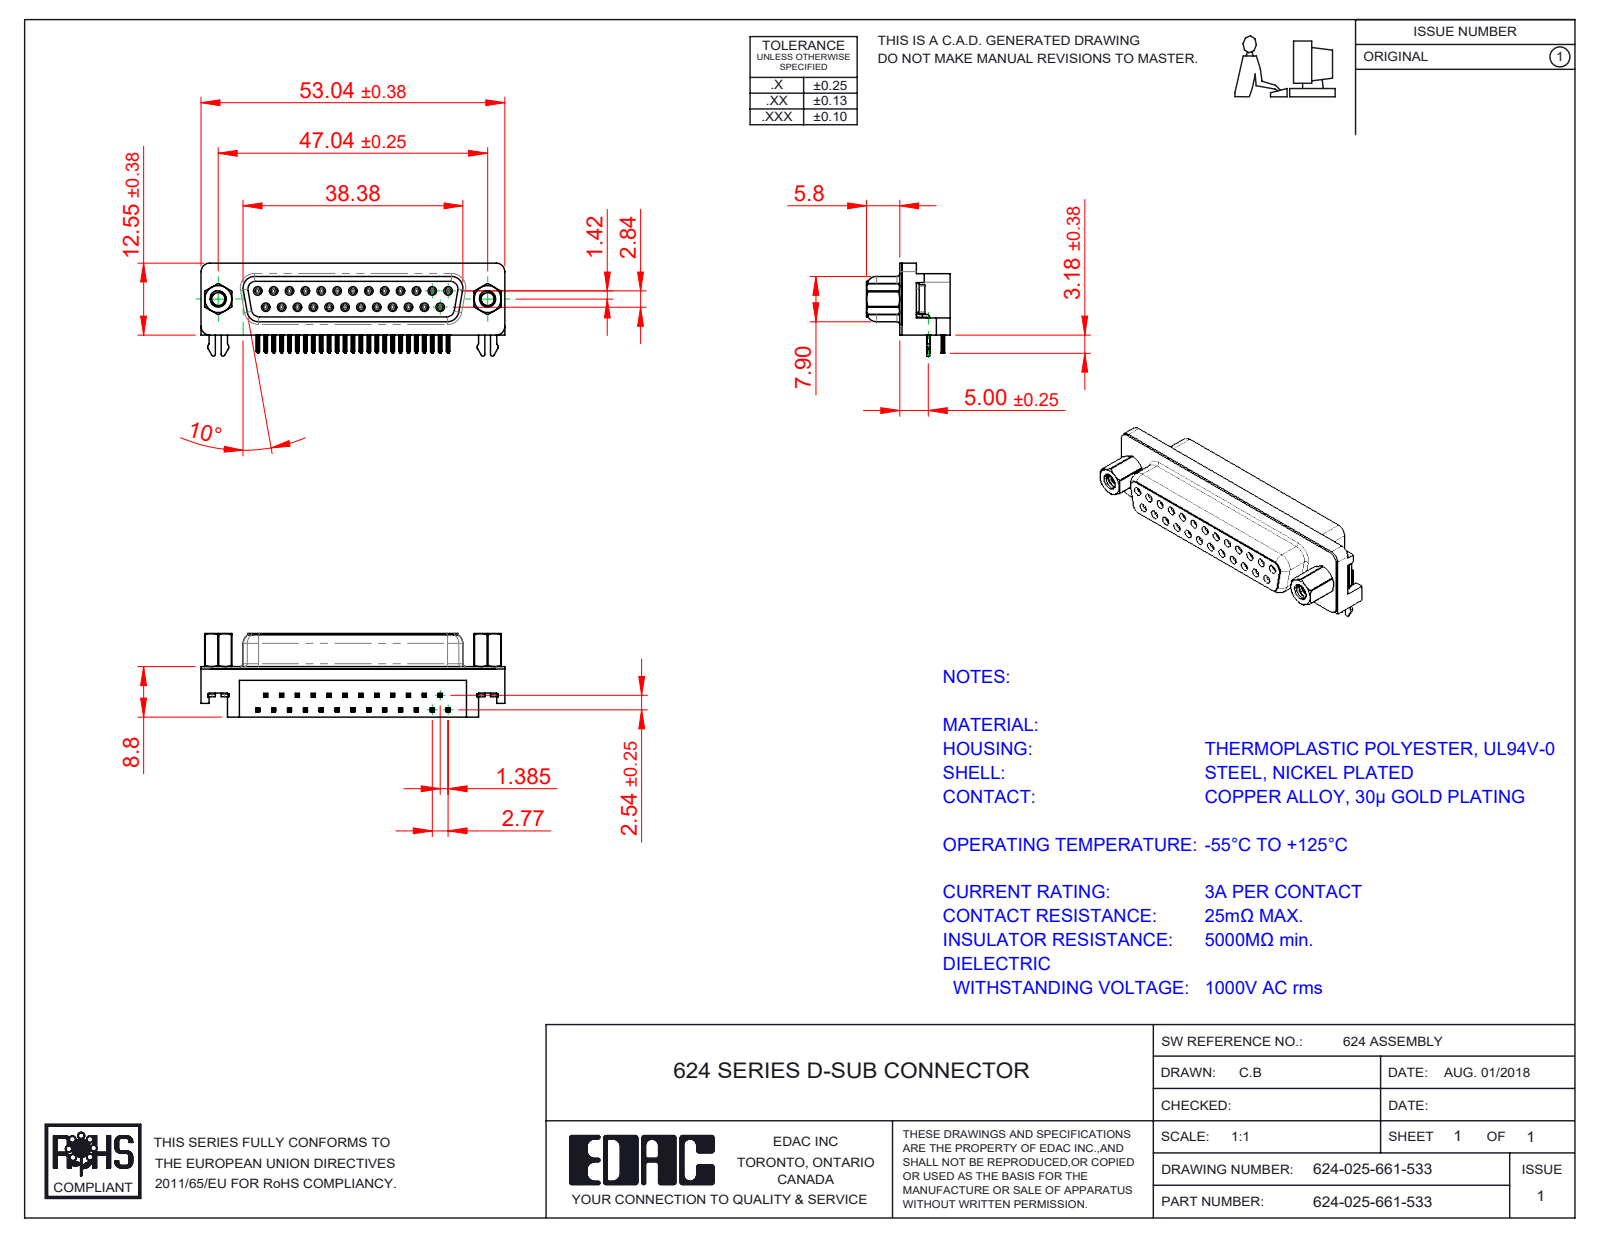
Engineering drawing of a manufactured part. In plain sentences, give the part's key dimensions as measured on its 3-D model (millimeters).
The part is named "624 Socket Bottom; 624-025-661-533; 624 Housing_25 Socket; 624 4-40 Threaded Rivet (+4 more)". Its 3-D file was written by "SolidWorks 2016 (CONFIG_CONTROL_DESIGN)". It is 33 solids with 3876 faces: 1652 planar, 982 cylindrical and 1242 other. Overall it measures 53.04 by 16.25 by 14.6 millimeters. Its volume is 6 170 cubic millimeters and its surface area 8 748 square millimeters. Round holes: 25 of diameter 0.8, 25 of diameter 0.9, 2 of diameter 2.26, 2 of diameter 2.29, 2 of diameter 4, 2 of diameter 4.8, 2 of diameter 5. Round bosses or shafts: 25 of diameter 1.2, 2 of diameter 4.9, 2 of diameter 4.75, 2 of diameter 3.9, 2 of diameter 2.79. Partial cylindrical surfaces (rounded edges, fillets, slot ends): 200 of radius 0.1, 100 of radius 0.15, 50 of radius 0.35, 25 of radius 0.34, 12 of radius 0.28, 10 of radius 0.5, 10 of radius 1, 8 of radius 0.25. The main face-to-face distances are 0.4, 6.2, 8.4, 8.8, 3.18, 9.38, 2.73, 2.9, 0.85, 7.05. The hole center spacings are 3.16, 2.77, 5.54, 8.31, 11.08, 5.03, 5.04, 7.48.
